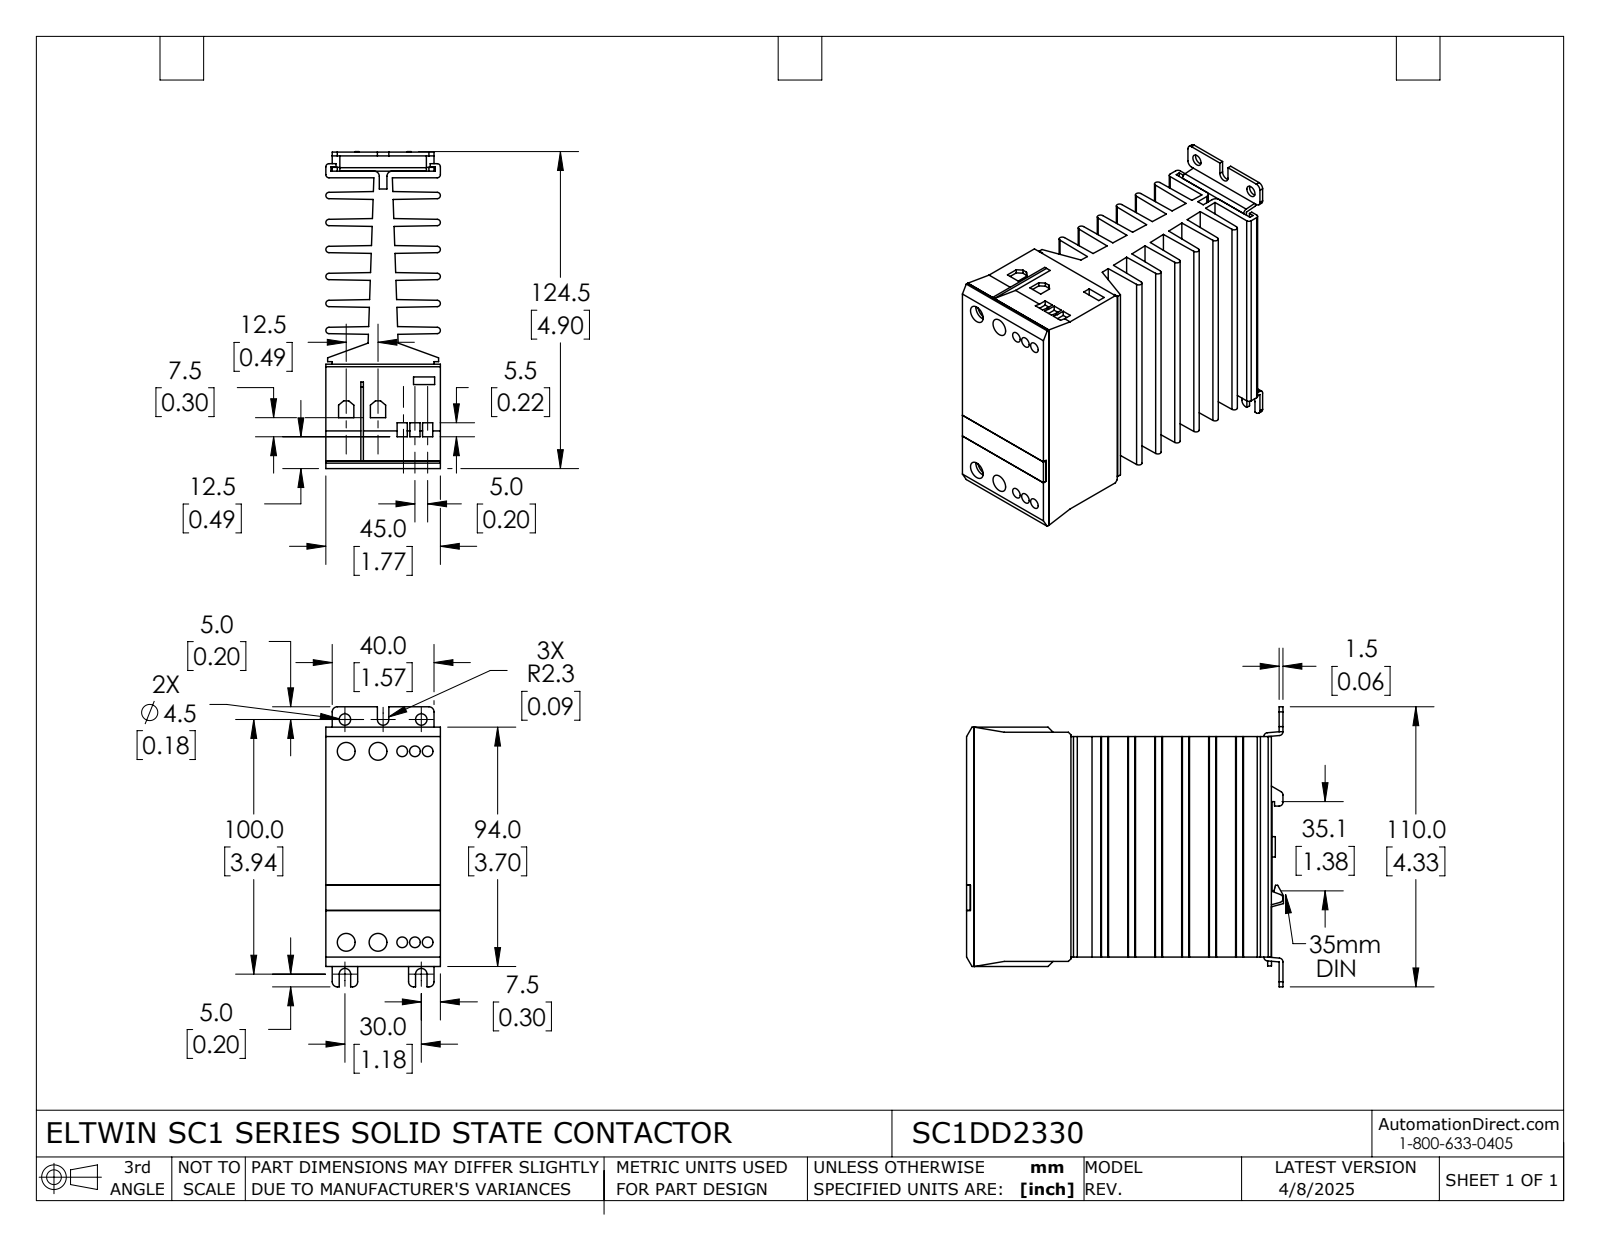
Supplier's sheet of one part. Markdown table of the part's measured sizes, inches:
| quantity | value |
| --- | --- |
| part name | SC1DD2330 |
| STEP written by | SolidWorks 2021 (AUTOMOTIVE_DESIGN) |
| units | inches |
| bodies | 7 solids, 391 faces (284 planar, 107 cylindrical, 0 other) |
| overall size | 4.902 × 4.331 × 1.772 |
| volume | 18.87 in³ |
| surface area | 165.4 in² |
| round holes (diameter × count) | 0.165 × 6, 0.173 × 6, 0.276 × 4, 0.177 × 2, 0.315 × 2 |
| round bosses / shafts (diameter × count) | 0.315 × 3 |
| partial cylindrical surfaces (radius × count) | 0.079 × 18, 0.049 × 16, 0.059 × 10, 0.051 × 4, 0.089 × 3 |
| main face-to-face distances | 0.417, 0.835, 0.127, 1.252, 0.29, 0.544, 0.707, 0.962, 1.669, 1.125 |
| hole center spacings | 2.953, 0.197, 2.959, 0.374, 0.394, 0.492, 0.502, 0.571 |
